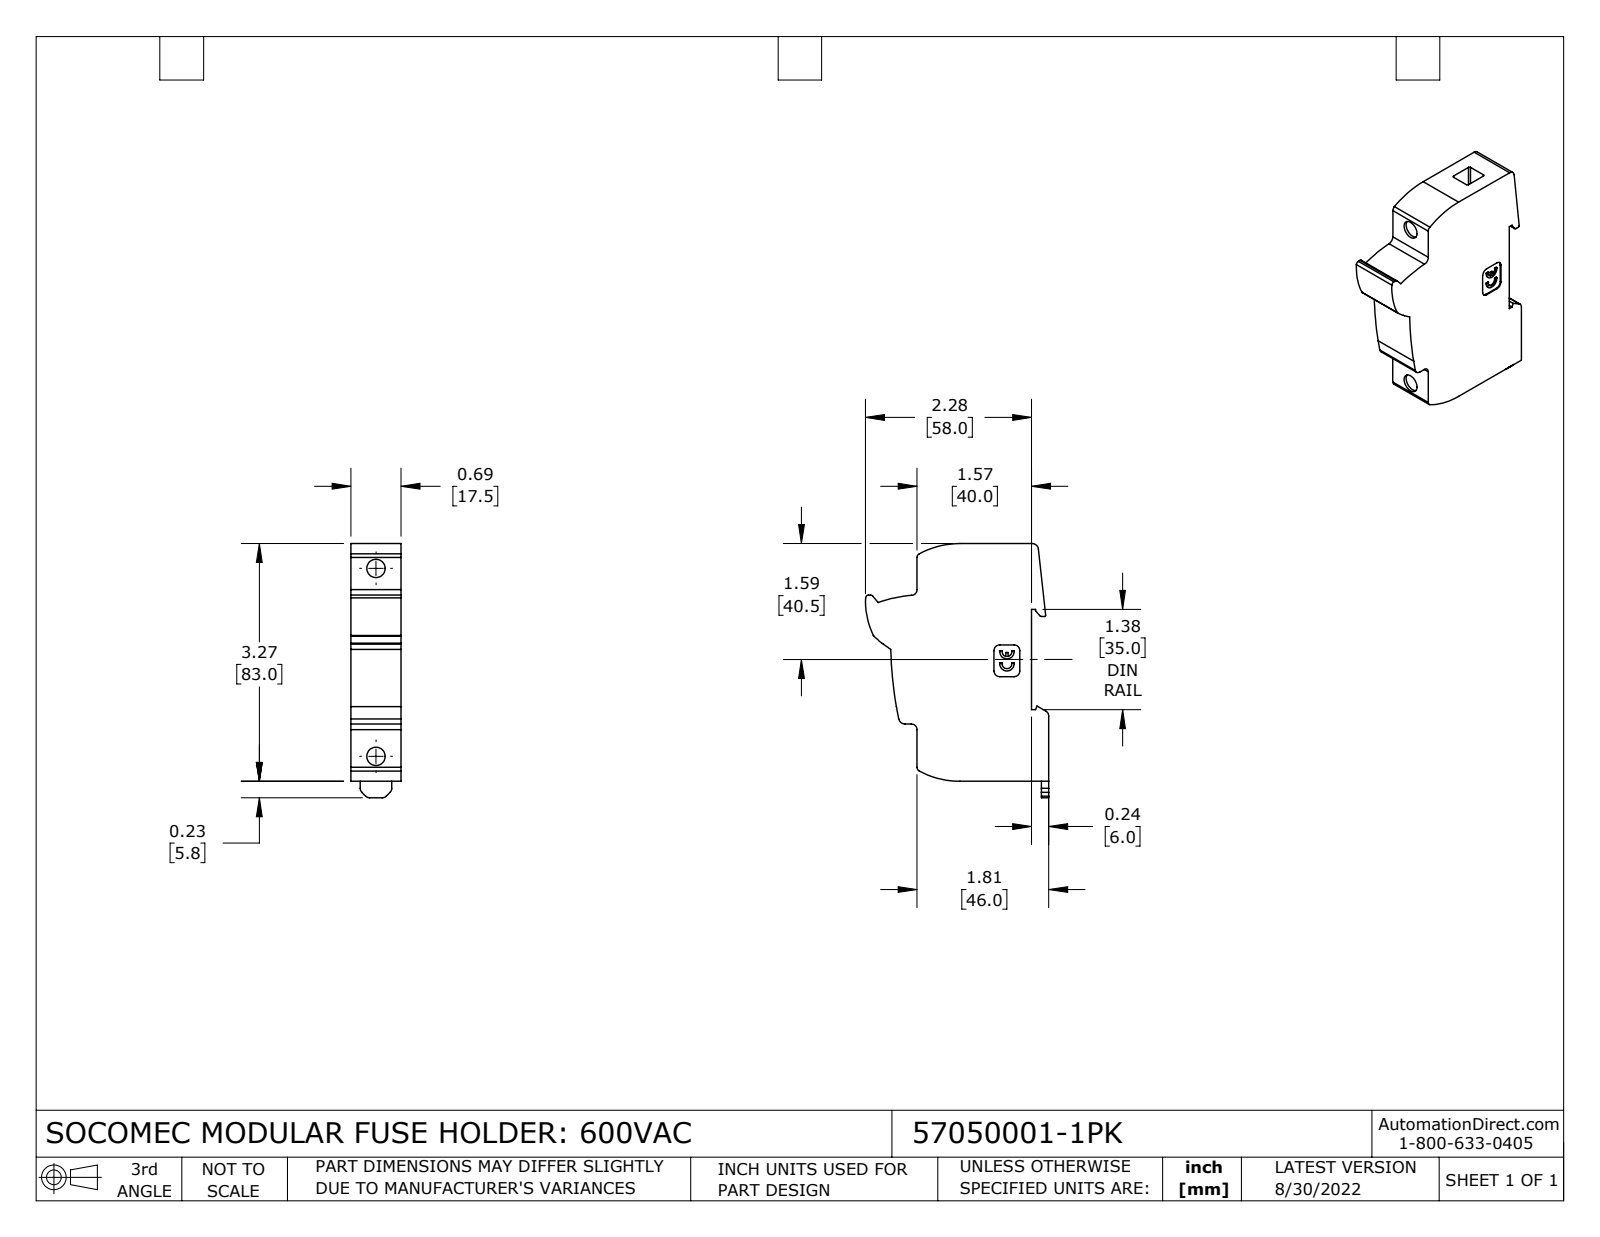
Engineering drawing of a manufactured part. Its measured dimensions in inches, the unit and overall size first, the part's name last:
Units: inches
Overall size (bounding box): 3.496 × 2.52 × 0.689
Round holes (diameter × count): ⌀0.252 ×2
Partial cylindrical surfaces — rounded edges, fillets, slot ends (radius × count): R0.079 ×11, R0.02 ×5, R0.039 ×4, R0.059 ×2, R0.067 ×2, R0.087 ×2, R0.098 ×2, R1.186 ×2
Main face-to-face distances: 0.689, 0.236, 1.575, 3.268, 1.811, 0.199, 0.49, 0.291, 0.518, 0.281
Hole centre spacings: 2.583
Volume: 4.229 in³ · Surface area: 21.33 in²
Bodies: 1 solid, 105 faces (52 planar, 53 cylindrical, 0 other)
Part name (STEP PRODUCT): 57050001-1PK
STEP written by: SolidWorks 2021 (CONFIG_CONTROL_DESIGN)
